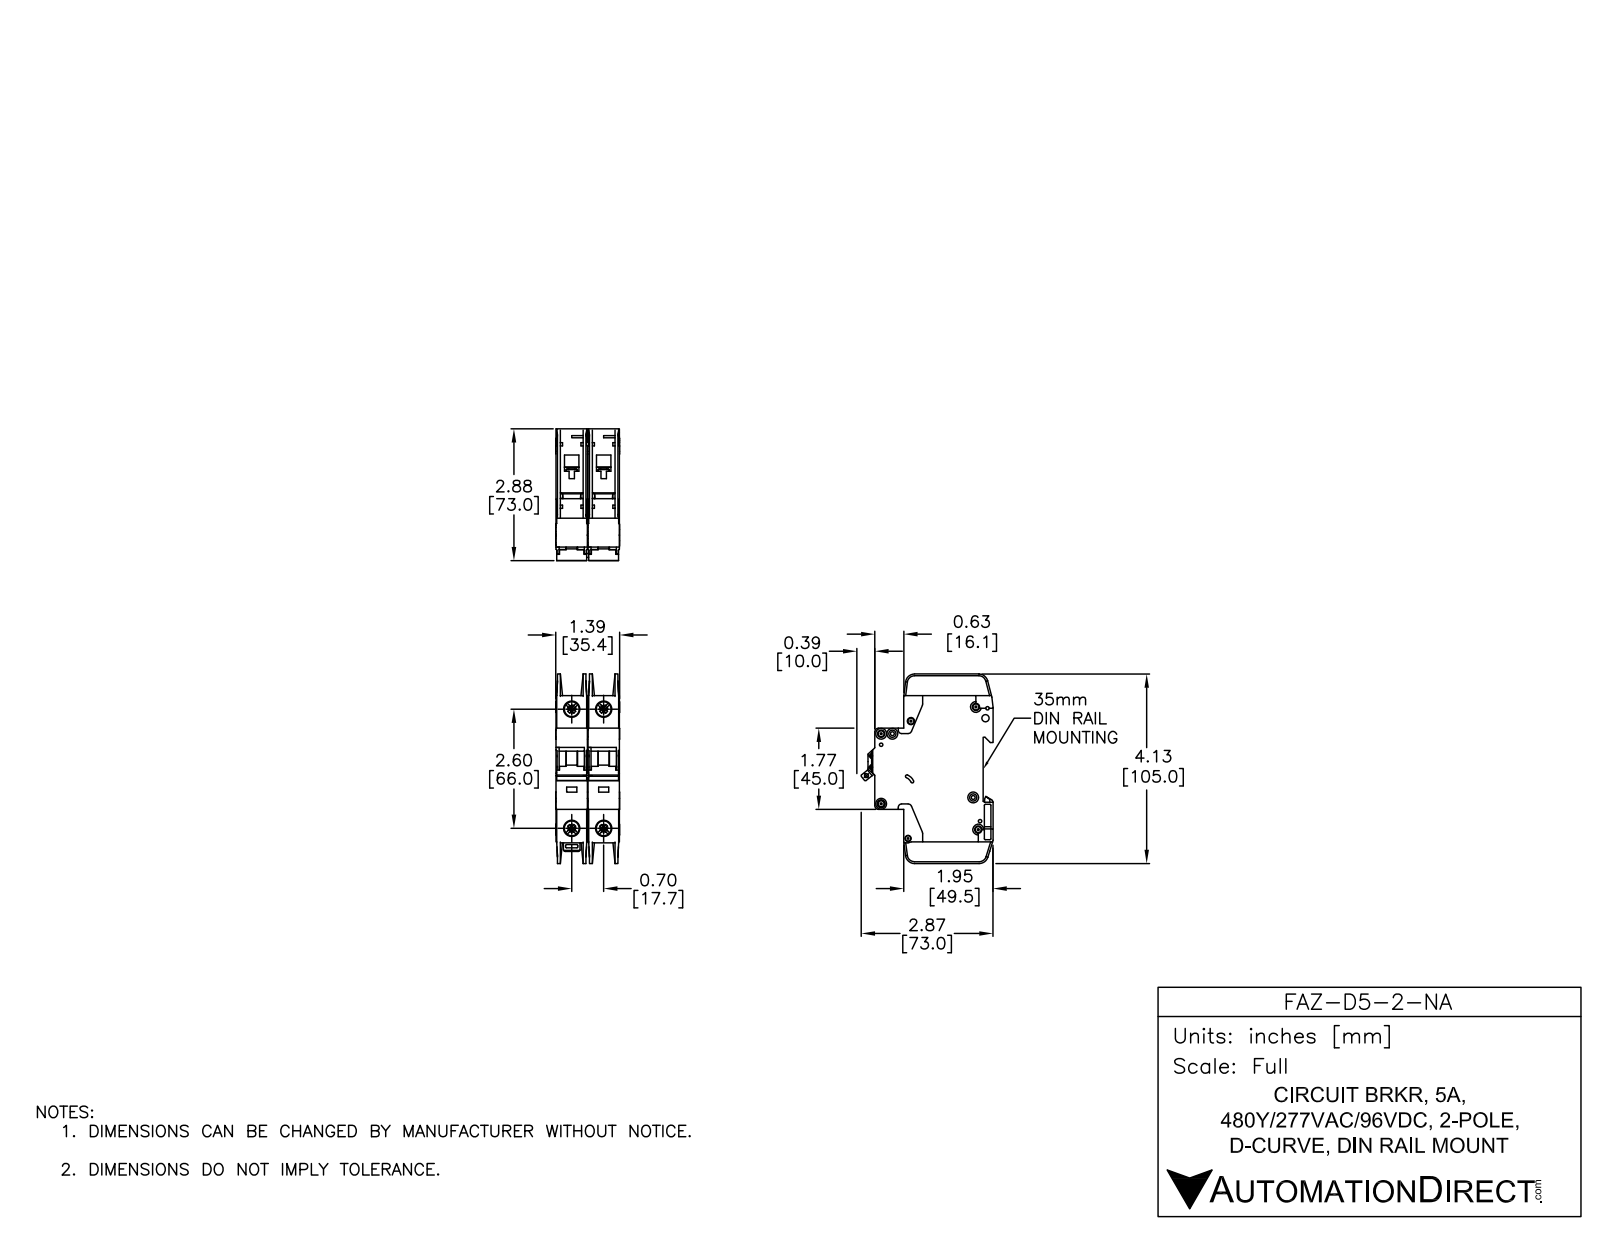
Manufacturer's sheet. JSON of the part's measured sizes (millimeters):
{"part_name": "FAZ-D5-2-NA", "step_written_by": "SolidWorks 2014 (AUTOMOTIVE_DESIGN)", "units": "millimeters", "bodies": {"solids": 6, "faces": 1568, "planar": 818, "cylindrical": 526, "other": 224}, "overall_size": [105, 73.04, 35.4], "volume_mm3": 155390, "surface_area_mm2": 49479, "round_holes": [[3.6, 7], [7.15, 4], [8.2, 4], [1.09, 2], [1.5, 2], [4, 2], [1.9, 1], [2.15, 1], [2.2, 1], [2.55, 1], [3.3, 1], [3.4, 1]], "round_bosses_or_shafts": [[6, 7], [2.5, 2]], "partial_cylinders_radius": [[0.25, 47], [0.5, 24], [1, 18], [2, 12], [5, 5], [1.8, 4], [4, 4], [0.2, 2]], "face_to_face_distances": [17.7, 17.5, 0.7, 15.05, 2.45, 1.75, 15.75, 13.3, 35.2, 17], "hole_center_spacings": [6.2, 17.7, 66, 68.33, 5.19, 6.1, 8.19, 8.56]}
